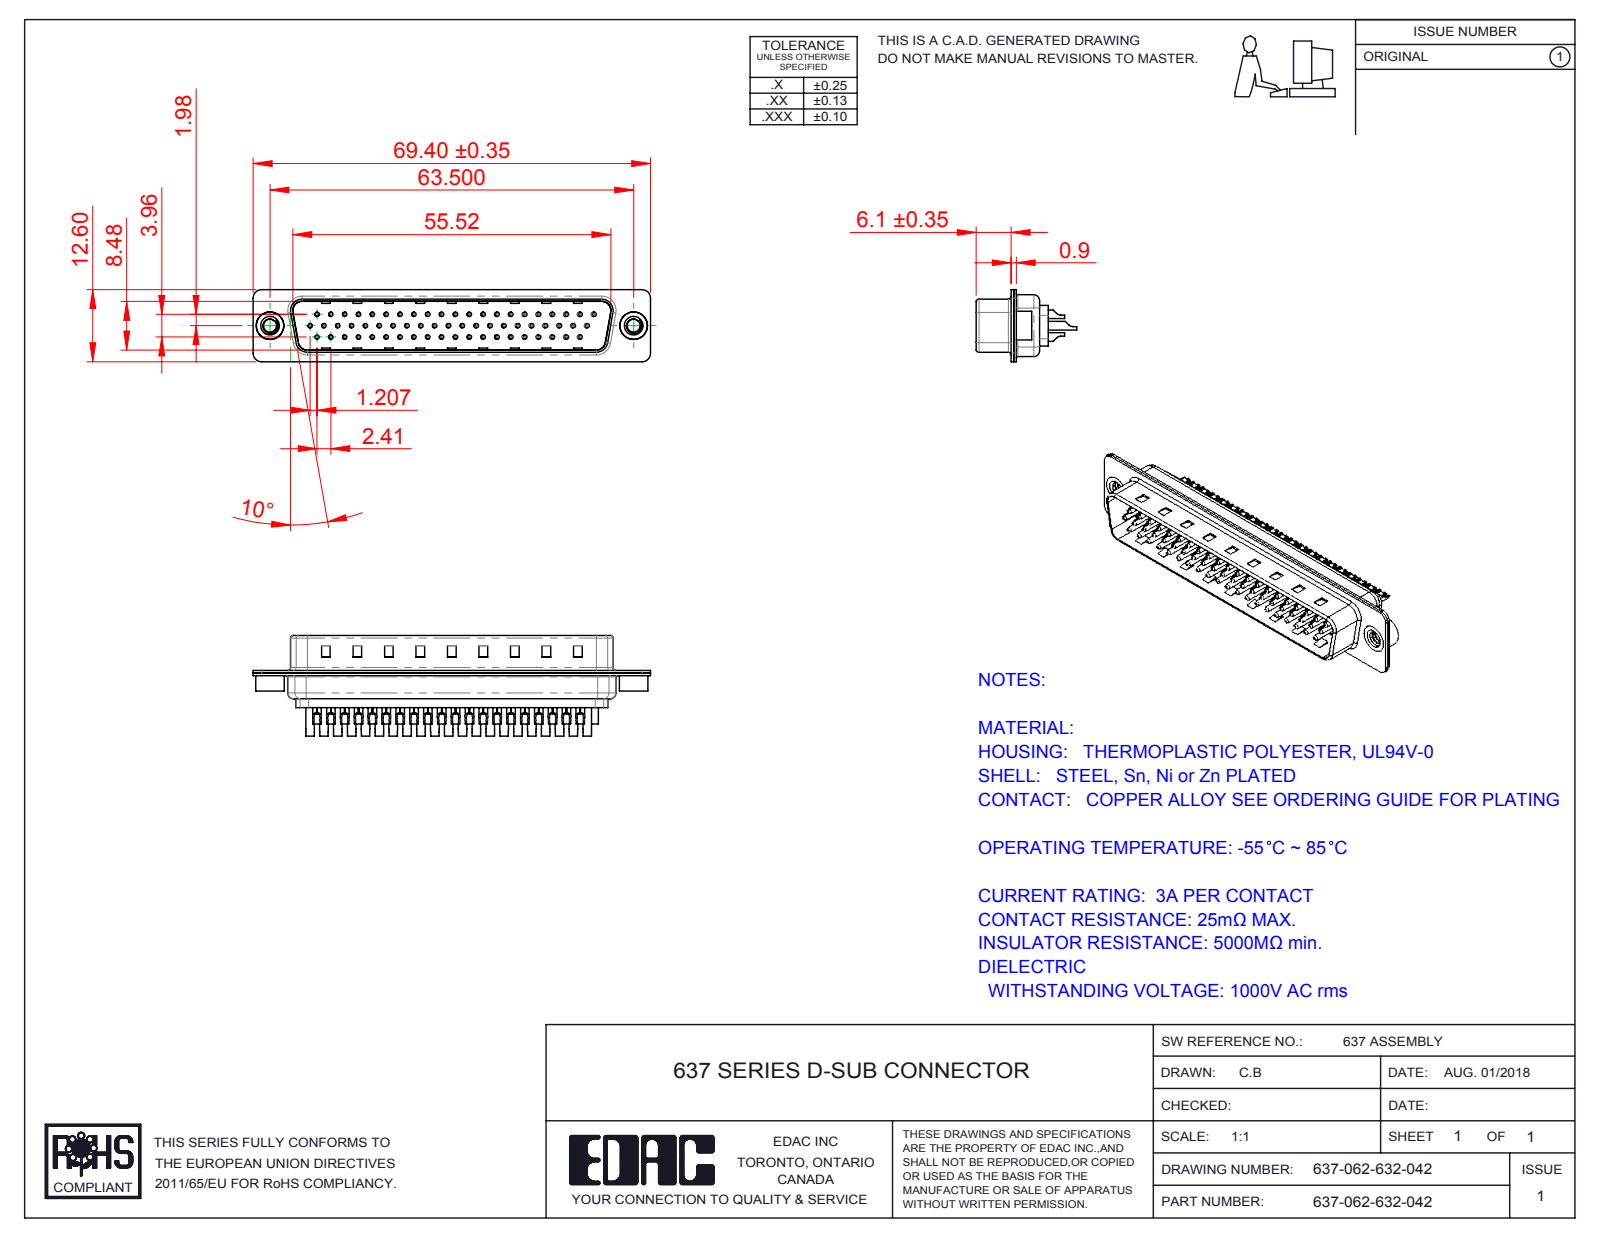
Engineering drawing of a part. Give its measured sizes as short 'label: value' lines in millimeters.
name: 637 Shell Rear_62 Contacts; 637-062-632-042; 637 4-40 Threaded Rivet; 637 Contact Row 2_32 (+4 more)
written by: SolidWorks 2016 (CONFIG_CONTROL_DESIGN)
unit: mm
bodies: 67 solids, 4380 faces (1071 planar, 1939 cylindrical, 1370 other)
size: 69.4 × 17.55 × 12.6
volume: 3 751 mm³; area: 14 173 mm²
holes: 119× ⌀1.6, 62× ⌀0.35, 62× ⌀1.1, 57× ⌀0.75, 57× ⌀2, 2× ⌀2.26, 2× ⌀4, 2× ⌀4.8
bosses: 62× ⌀2, 62× ⌀1.5, 62× ⌀0.75, 2× ⌀5, 2× ⌀4.9
rounds: 16× R1.5, 12× R2, 8× R0.5, 7× R1, 4× R0.25, 4× R0.55, 4× R0.7, 4× R0.95
face distances: 0.45, 0.4, 0.7, 8.88, 8.48, 0.9, 0.31, 0.76, 1.16, 0.71
hole spacings: 7.24, 2.32, 2.41, 4.13, 9.65, 4.83, 14.48, 11.04
